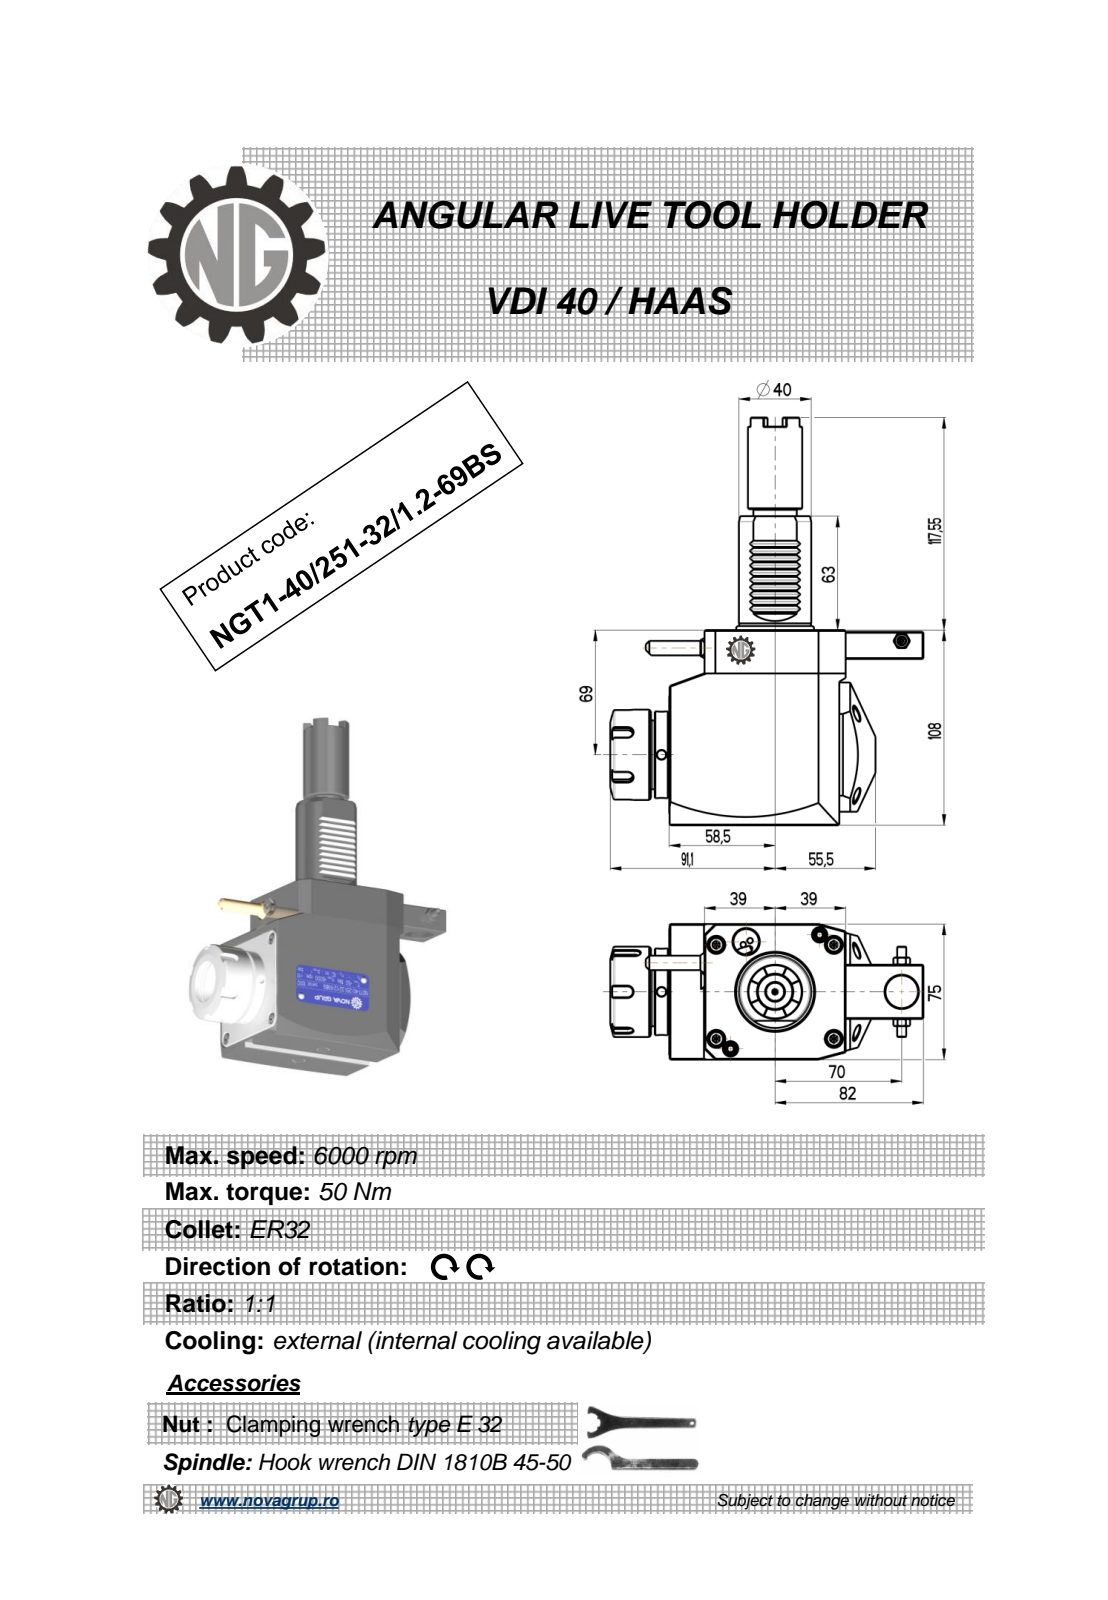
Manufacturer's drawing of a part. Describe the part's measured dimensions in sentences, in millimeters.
The part is named "NGT1_40_251_32_1_2_69BS". Its 3-D file was written by "PRO/ENGINEER BY PARAMETRIC TECHNOLOGY CORPORATION, 2010280 (CONFIG_CONTROL_DESIGN)". It is 1 solid with 475 faces: 236 planar, 100 cylindrical and 139 other. Overall it measures 225.55 by 173.1 by 76.6 millimeters. Its volume is 954 611 cubic millimeters and its surface area 79 386 square millimeters. Round holes: 3 of diameter 5, 1 of diameter 3, 1 of diameter 4.2, 1 of diameter 9.5, 1 of diameter 18, 1 of diameter 27. Round bosses or shafts: 1 of diameter 50, 1 of diameter 48, 1 of diameter 41.5, 1 of diameter 41, 1 of diameter 40, 1 of diameter 30, 1 of diameter 24, 1 of diameter 10. Partial cylindrical surfaces (rounded edges, fillets, slot ends): 12 of radius 0.26, 10 of radius 0.3, 6 of radius 0.2, 5 of radius 3, 2 of radius 5.8, 2 of radius 6, 2 of radius 600, 1 of radius 0.5. The main face-to-face distances are 75, 108, 1, 22.5, 3.5, 19.5, 20, 97.5, 78, 19.3. The hole center spacings are 16.19, 61.13, 61.5, 132.75, 146.94.
